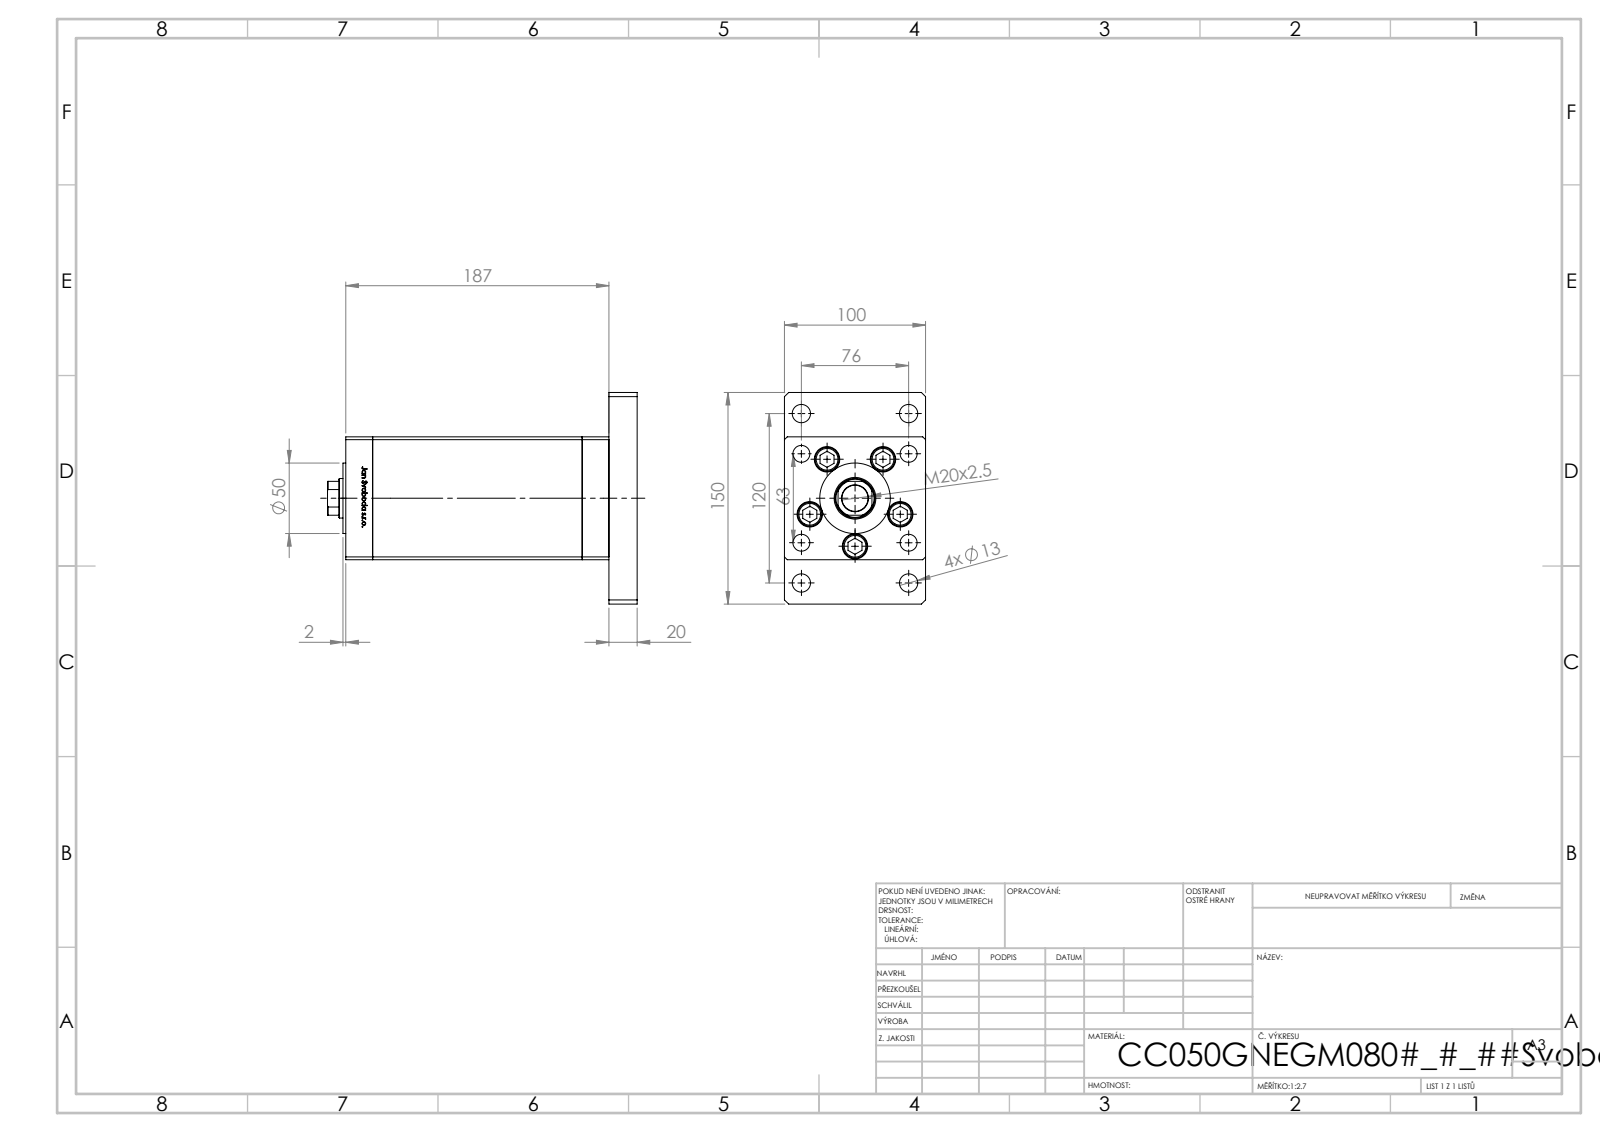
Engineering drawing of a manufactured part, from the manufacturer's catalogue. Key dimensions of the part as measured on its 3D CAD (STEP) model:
Part name (STEP PRODUCT): V220C BACK_G; V220C_G_MIDDLE; V220C_FRONT_G; ALLEN BOLT (+2 more)
STEP written by: SolidWorks 2019 (CONFIG_CONTROL_DESIGN)
Units: millimetres
Bodies: 19 solids, 1310 faces (517 planar, 187 cylindrical, 606 other)
Overall size (bounding box): 219.5 × 150 × 100
Volume: 1 697 000 mm³ · Surface area: 256 566 mm²
Round holes (diameter × count): ⌀12 ×9, ⌀13.5 ×5, ⌀18 ×5, ⌀13 ×4, ⌀17 ×4, ⌀2 ×2, ⌀13.16 ×2, ⌀18.5 ×1, ⌀28 ×1, ⌀29.5 ×1, ⌀68 ×1
Round bosses / shafts (diameter × count): ⌀8 ×9, ⌀17 ×5, ⌀50 ×1
Partial cylindrical surfaces — rounded edges, fillets, slot ends (radius × count): R0.93 ×2, R13.5 ×1
Main face-to-face distances: 19, 100, 167.5, 87, 148.5, 20, 187.5, 39, 206.5, 186.5
Hole centre spacings: 34, 28.5, 49.36, 71.02, 76, 81.17, 91.5, 118.95
